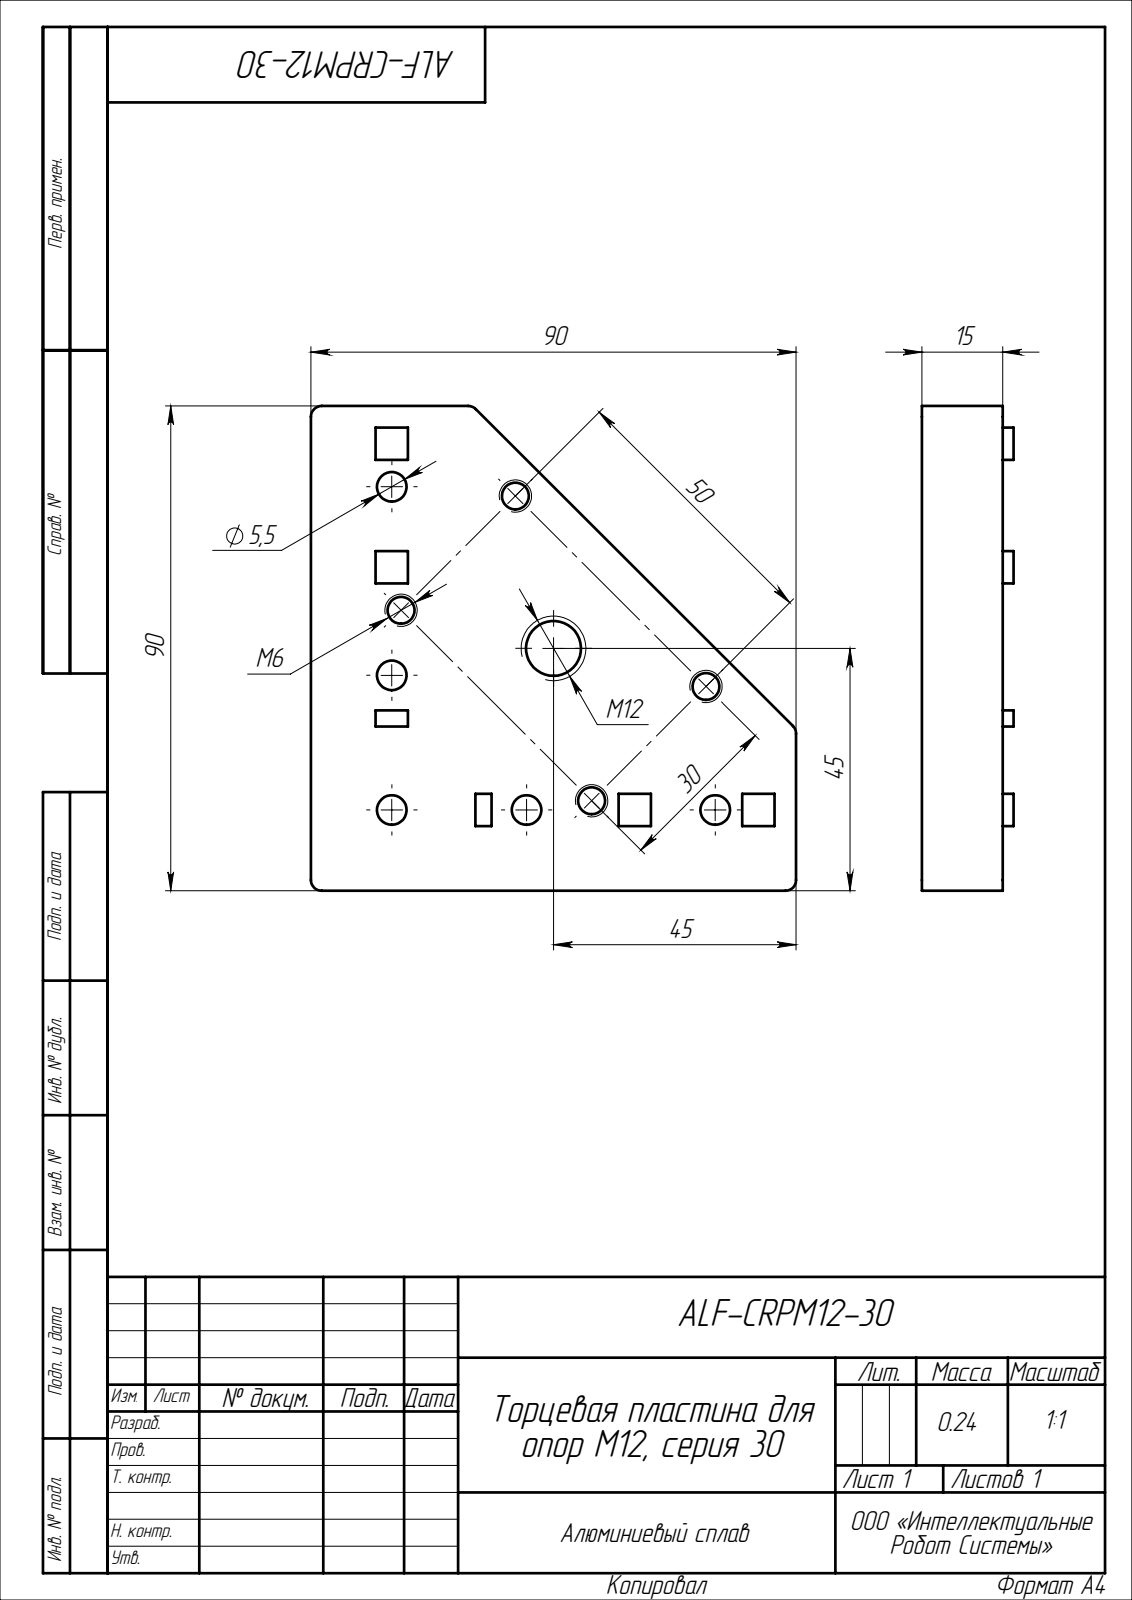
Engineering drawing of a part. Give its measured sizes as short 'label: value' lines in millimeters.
name: ALF-CRPM12-30
written by: SolidWorks 2022 (CONFIG_CONTROL_DESIGN)
unit: mm
bodies: 1 solid, 62 faces (37 planar, 25 cylindrical, 0 other)
size: 90 × 90 × 17
volume: 90 633 mm³; area: 19 851 mm²
holes: 5× ⌀5.5, 4× ⌀5, 1× ⌀10.2
rounds: 5× R2
face distances: 15, 90, 17, 2, 6, 78, 12, 72, 18, 68
hole spacings: 22.99, 29.15, 69.07, 42.43, 12.19, 25, 30, 30.41
